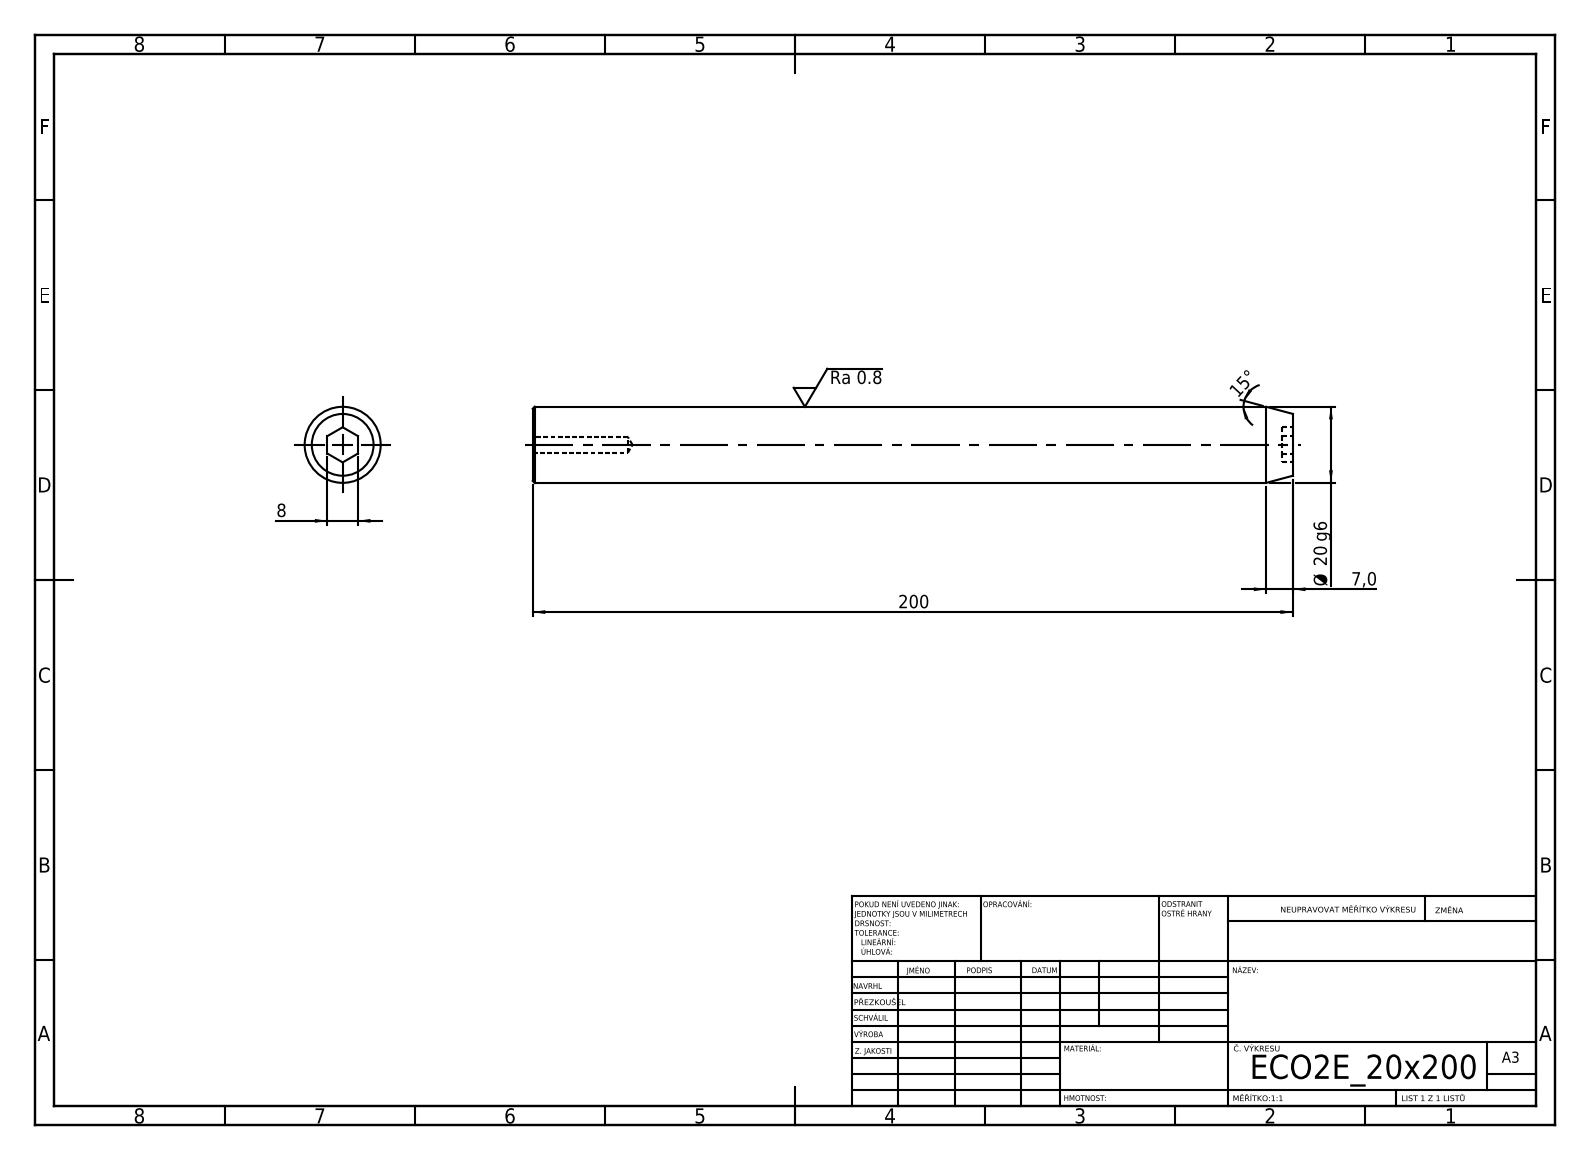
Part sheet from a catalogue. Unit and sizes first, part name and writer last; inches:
Units: inches
Overall size (bounding box): 7.874 × 0.787 × 0.787
Round holes (diameter × count): ⌀0.165 ×1
Round bosses / shafts (diameter × count): ⌀0.787 ×1
Main face-to-face distances: 7.874, 0.11, 7.764, 0.315
Volume: 3.779 in³ · Surface area: 20.85 in²
Bodies: 1 solid, 19 faces (9 planar, 4 cylindrical, 6 other)
STEP written by: SolidWorks 2019 (CONFIG_CONTROL_DESIGN)
